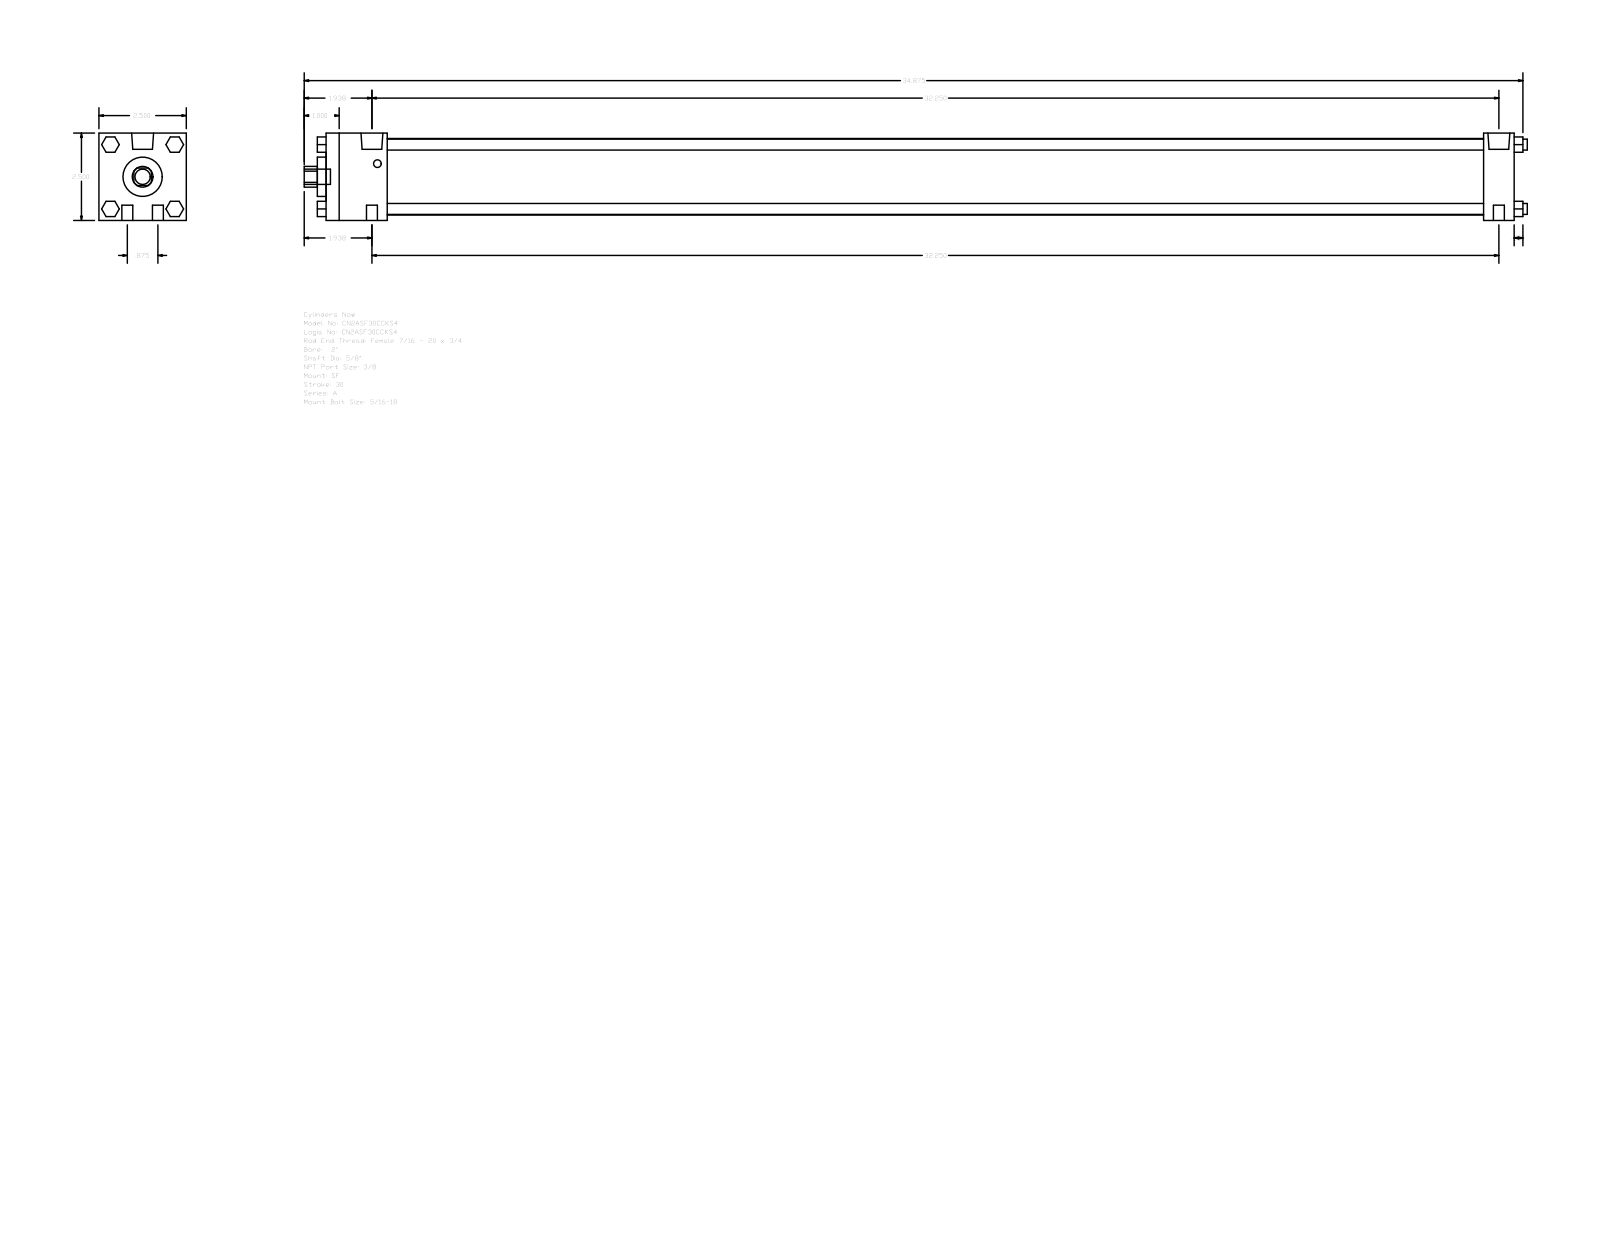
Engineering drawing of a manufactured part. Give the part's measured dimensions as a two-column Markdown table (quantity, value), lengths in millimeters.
| quantity | value |
| --- | --- |
| part name | A_SF__0200_0.625 |
| STEP written by | GSSL Pune (CONFIG_CONTROL_DESIGN) |
| units | millimeters |
| bodies | 0 solids, 124 faces (94 planar, 30 cylindrical, 0 other) |
| overall size | 889 × 63.5 × 63.5 |
| round holes (diameter × count) | 15.88 × 1, 28.57 × 1, 55.63 × 1 |
| round bosses / shafts (diameter × count) | 7.94 × 8, 15.93 × 2, 5.56 × 2, 11.11 × 1 |
| partial cylindrical surfaces (radius × count) | 7.54 × 1 |
| main face-to-face distances | 63.5, 863.6, 841.37, 22.23, 44.45, 796.92, 819.15, 869.95, 6.35, 50.8 |
